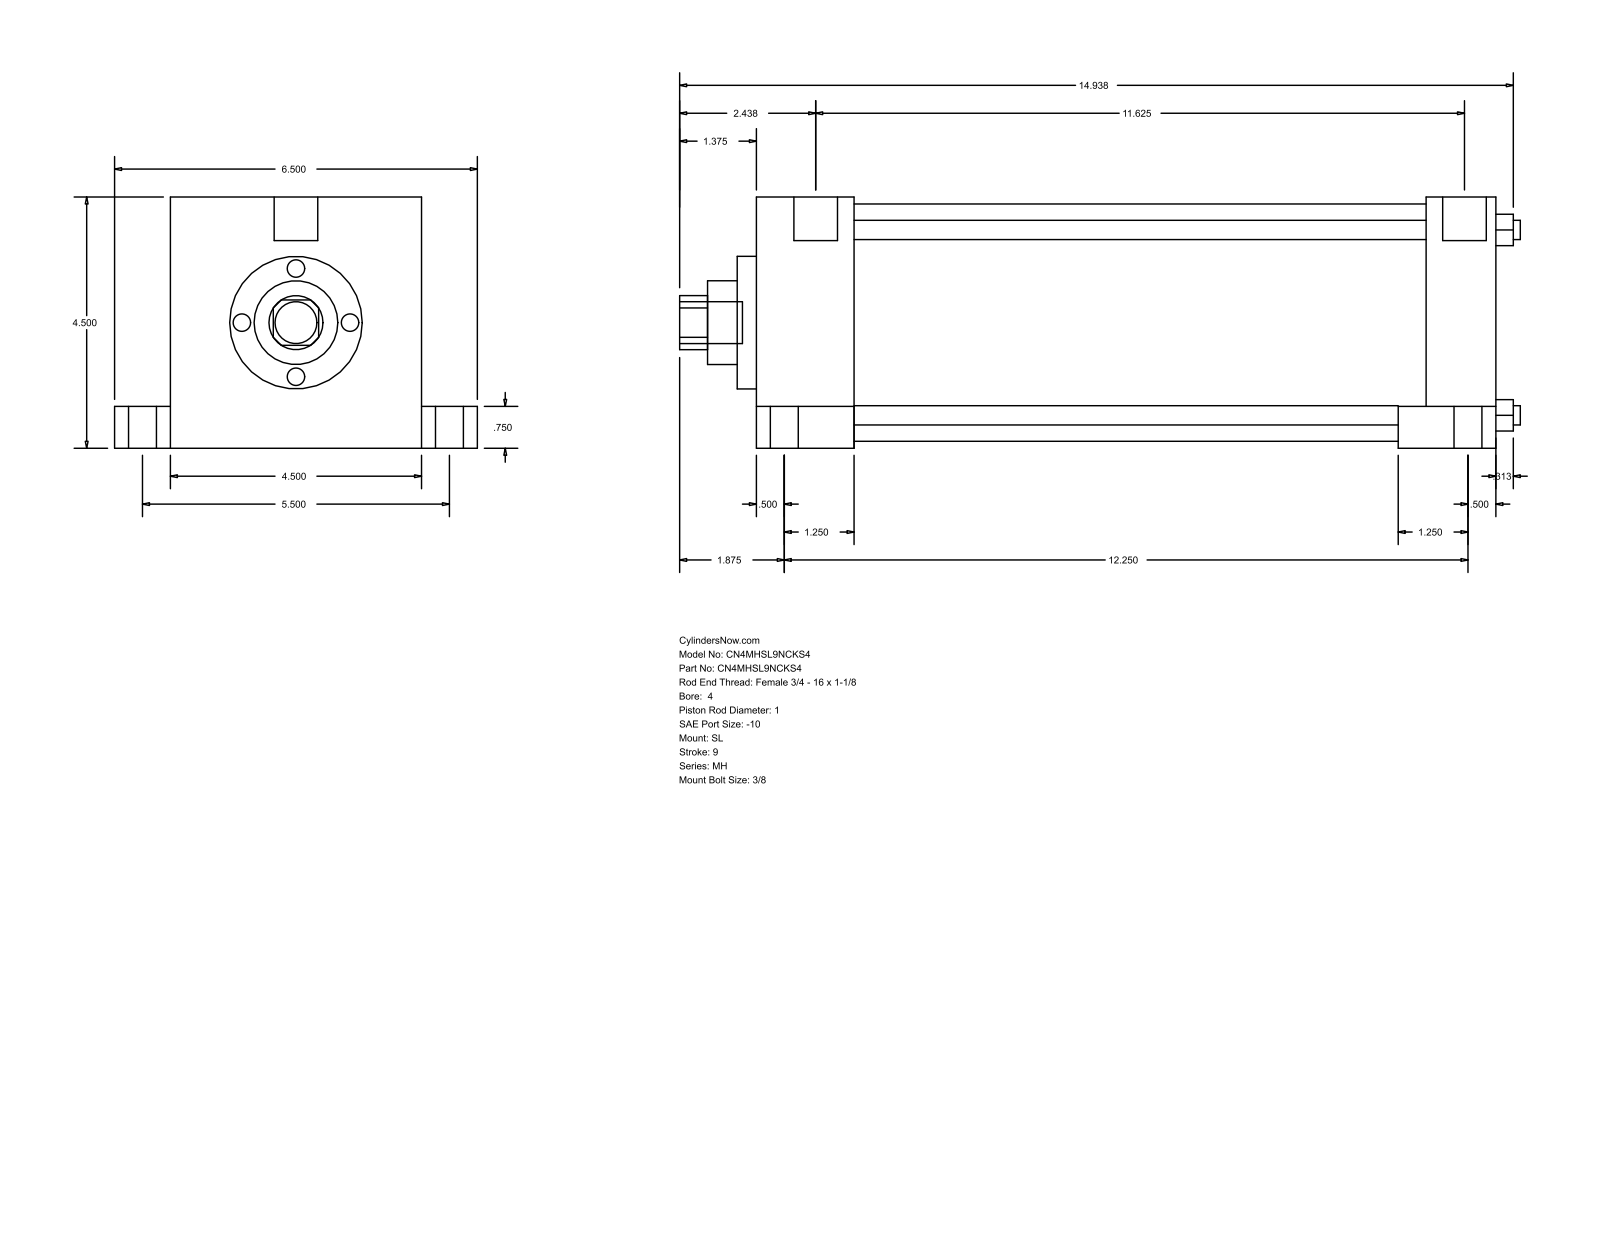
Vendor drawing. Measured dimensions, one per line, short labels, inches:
name: MH_SL__0400_1
written by: GSSL Pune (CONFIG_CONTROL_DESIGN)
unit: in
bodies: 0 solids, 110 faces (77 planar, 33 cylindrical, 0 other)
size: 15.063 × 6.5 × 4.5
holes: 4× ⌀0.345, 1× ⌀1, 1× ⌀1.5, 1× ⌀2.375, 1× ⌀4.25
bosses: 5× ⌀0.75, 4× ⌀0.5, 4× ⌀0.344, 2× ⌀0.781
rounds: 1× R0.484
face distances: 4.5, 13.25, 1.75, 11.5, 12, 10.25, 1.25, 1, 5.5, 0.75
hole spacings: 2.347, 3.32, 4.695
